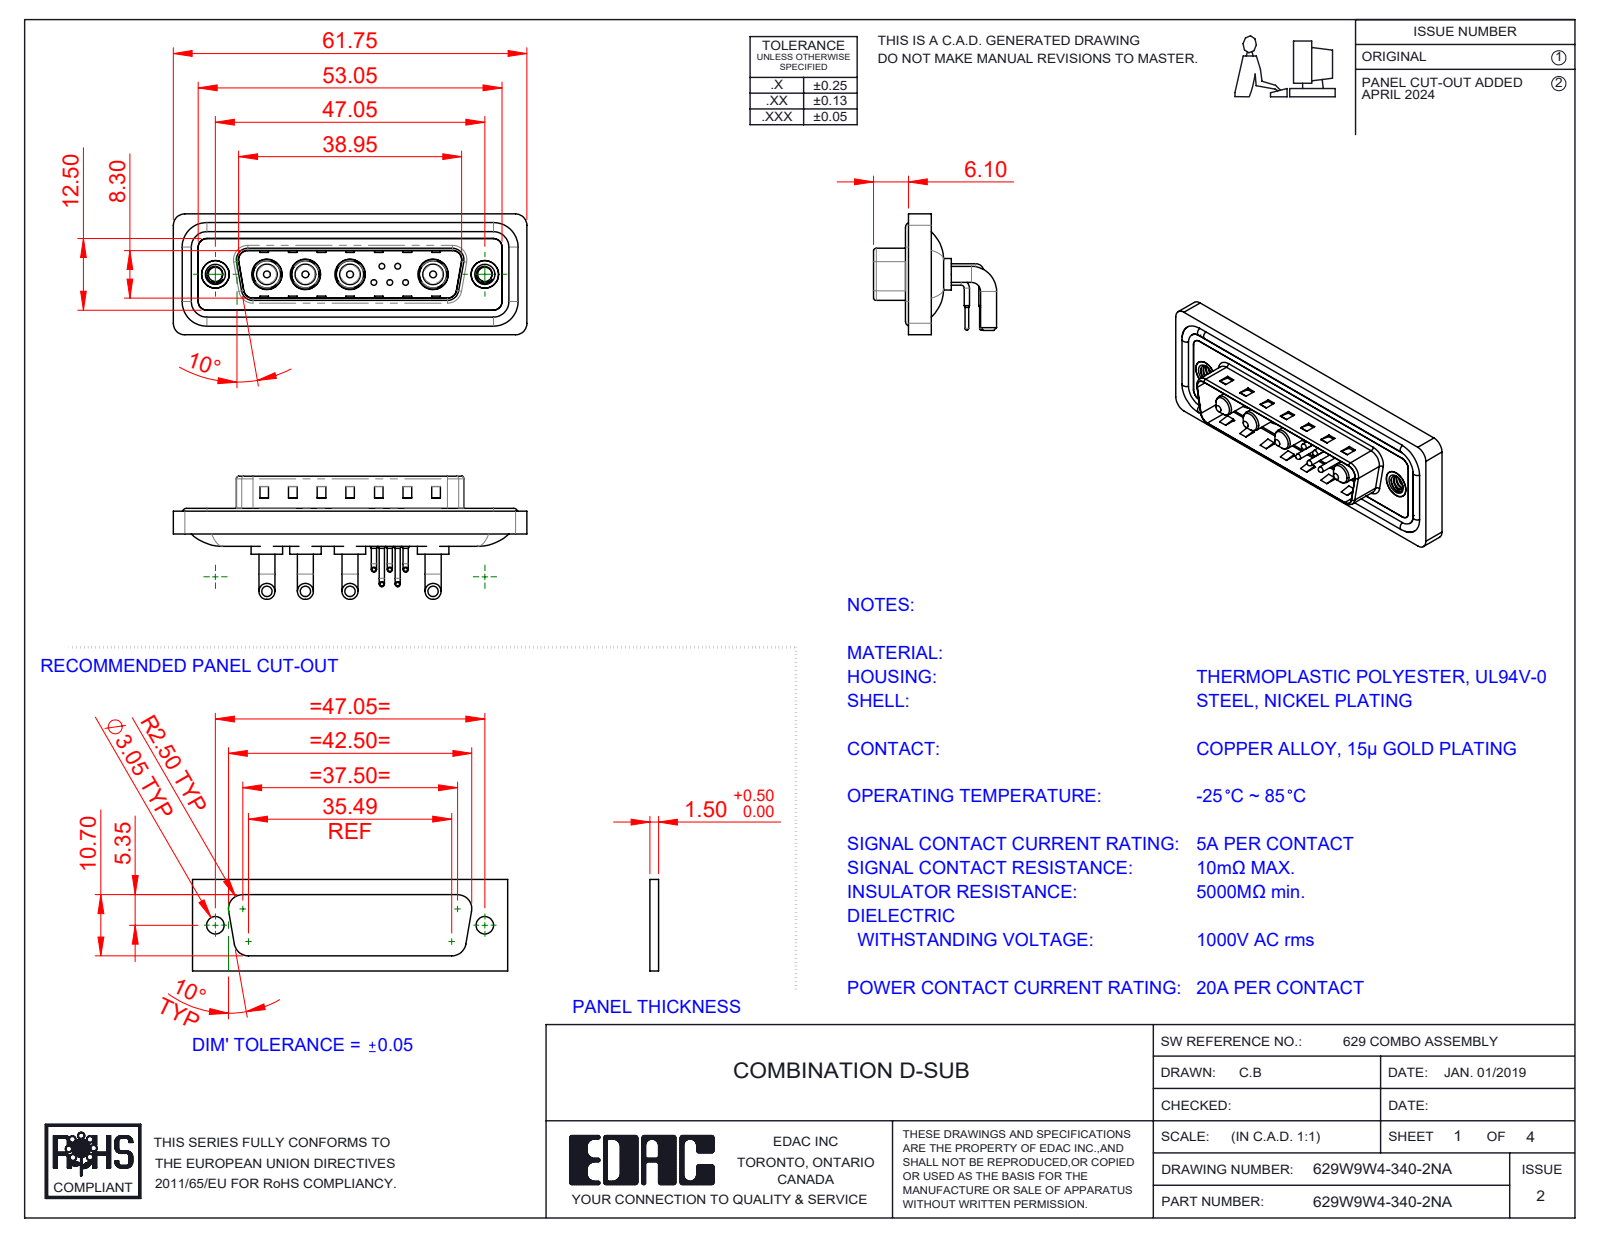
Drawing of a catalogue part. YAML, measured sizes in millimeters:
part_name: "629Combo Contact Row 2; 629Combo Shell Rear_25 Contacts; Power Pin_20A RA; 629Combo Threaded Rivet_A (+5 more)"
step_written_by: "SolidWorks 2023 (CONFIG_CONTROL_DESIGN)"
units: millimeters
bodies: {solids: 20, faces: 1199, planar: 569, cylindrical: 450, other: 180}
overall_size: [61.75, 21.5, 21.1]
volume: 7708
surface_area: 12380
round_holes:
  - {diameter: 0.75, count: 5}
  - {diameter: 1.6, count: 5}
  - {diameter: 2, count: 5}
  - {diameter: 4.85, count: 4}
  - {diameter: 5.3, count: 4}
  - {diameter: 2.5, count: 2}
  - {diameter: 4, count: 2}
  - {diameter: 4.8, count: 2}
  - {diameter: 5, count: 2}
round_bosses_or_shafts:
  - {diameter: 0.9, count: 10}
  - {diameter: 2.8, count: 8}
  - {diameter: 1.5, count: 5}
  - {diameter: 1, count: 5}
  - {diameter: 0.65, count: 5}
  - {diameter: 5.5, count: 4}
  - {diameter: 5.2, count: 4}
  - {diameter: 4.75, count: 4}
partial_cylinders:
  - {radius: 1.5, count: 18}
  - {radius: 2, count: 18}
  - {radius: 0.5, count: 8}
  - {radius: 1.6, count: 8}
  - {radius: 1.01, count: 5}
  - {radius: 0.25, count: 4}
  - {radius: 0.6, count: 4}
  - {radius: 0.65, count: 4}
face_to_face_distances: [0.4, 2.9, 0.8, 4.1, 1.1, 4.5, 2.1, 1.6, 1.5, 3.1]
hole_center_spacings: [3.16, 2.77, 5.04, 14.5, 2.78, 4.4, 4.41, 5]
